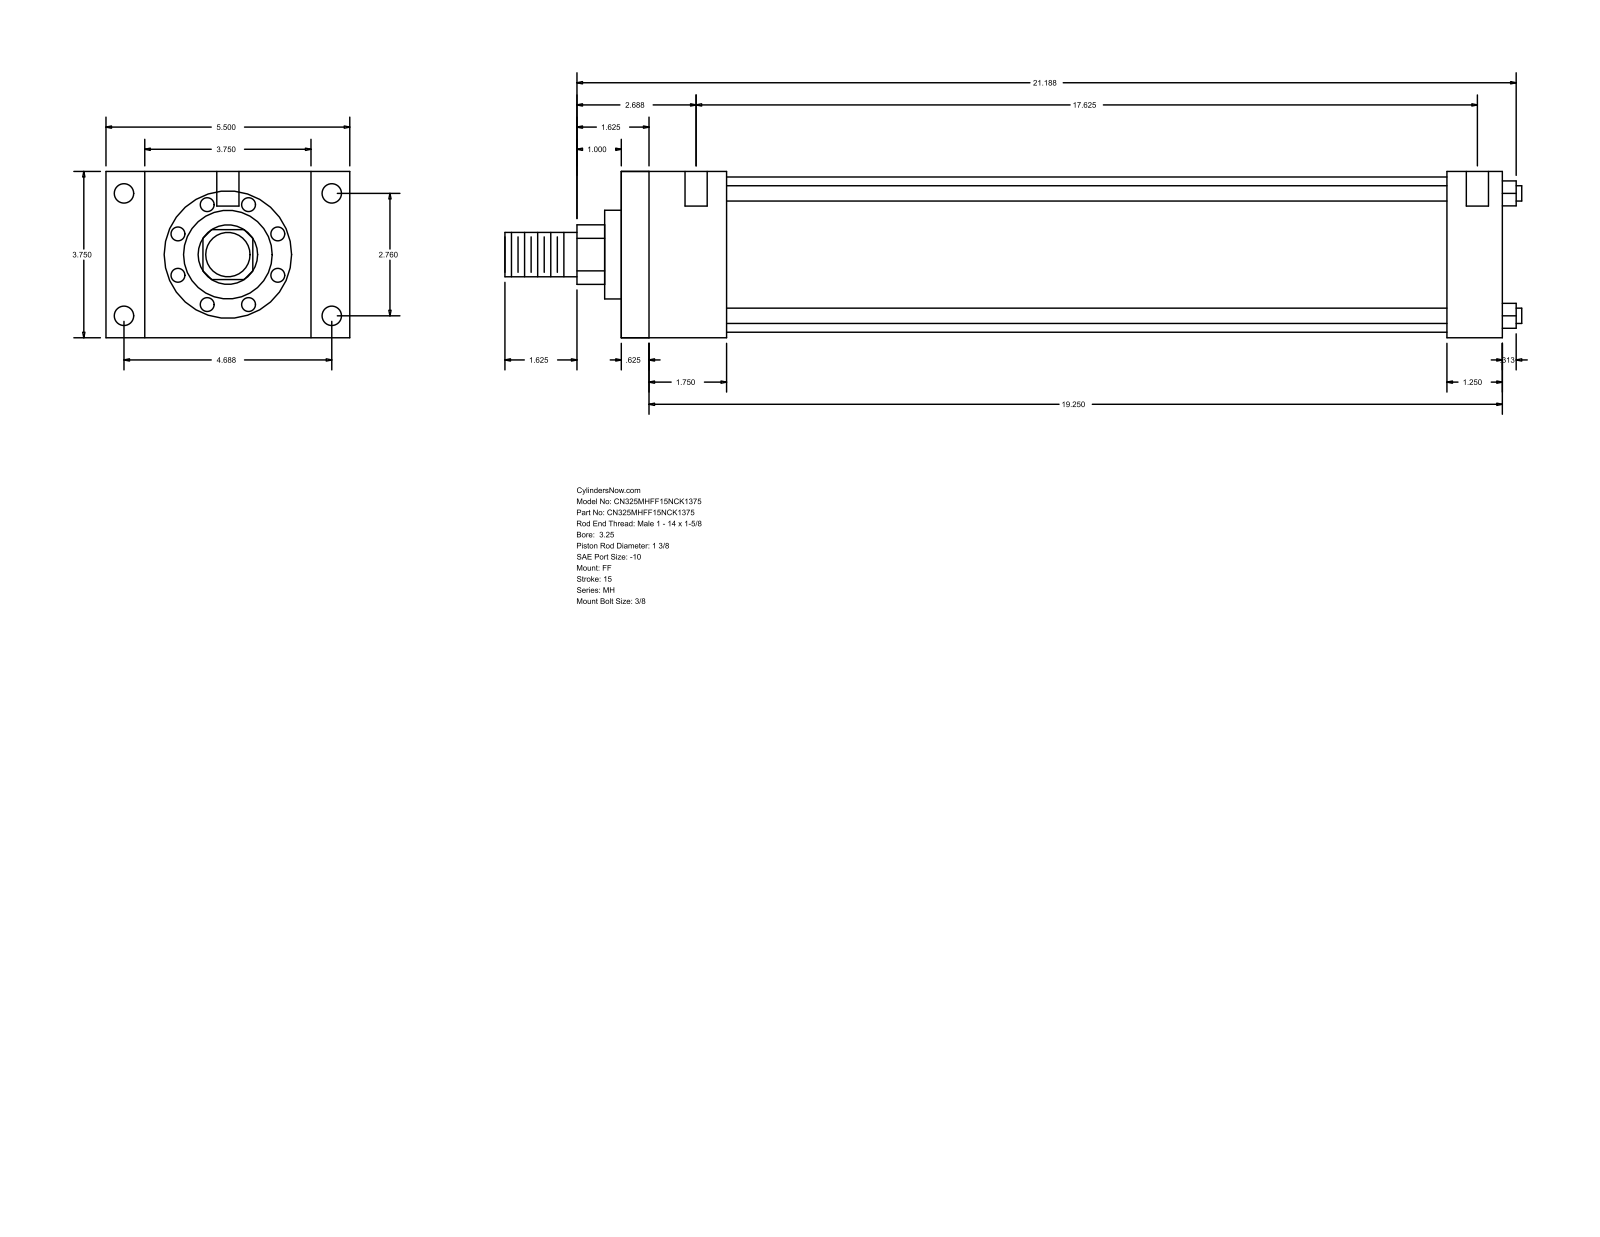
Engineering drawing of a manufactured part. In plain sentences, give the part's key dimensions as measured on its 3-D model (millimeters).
The part is named "MH_FF__0325_1.375". Its 3-D file was written by "GSSL Pune (CONFIG_CONTROL_DESIGN)". It is 0 solids with 92 faces: 64 planar, 28 cylindrical and 0 other. Overall it measures 582.61 by 139.7 by 95.25 millimeters. Round holes: 4 of diameter 5.56, 4 of diameter 11.13, 2 of diameter 12.7. Round bosses or shafts: 4 of diameter 8.76, 1 of diameter 88.9, 1 of diameter 50.8, 1 of diameter 34.92, 1 of diameter 25.4. Partial cylindrical surfaces (rounded edges, fillets, slot ends): 1 of radius 17.06. The main face-to-face distances are 95.24, 504.83, 15.87, 488.96, 22.23, 117.47, 473.08, 457.21, 31.75, 60.32. The hole center spacings are 70.1, 119.06, 138.16, 454.03, 1.59, 4.76, 447.68, 449.27.
